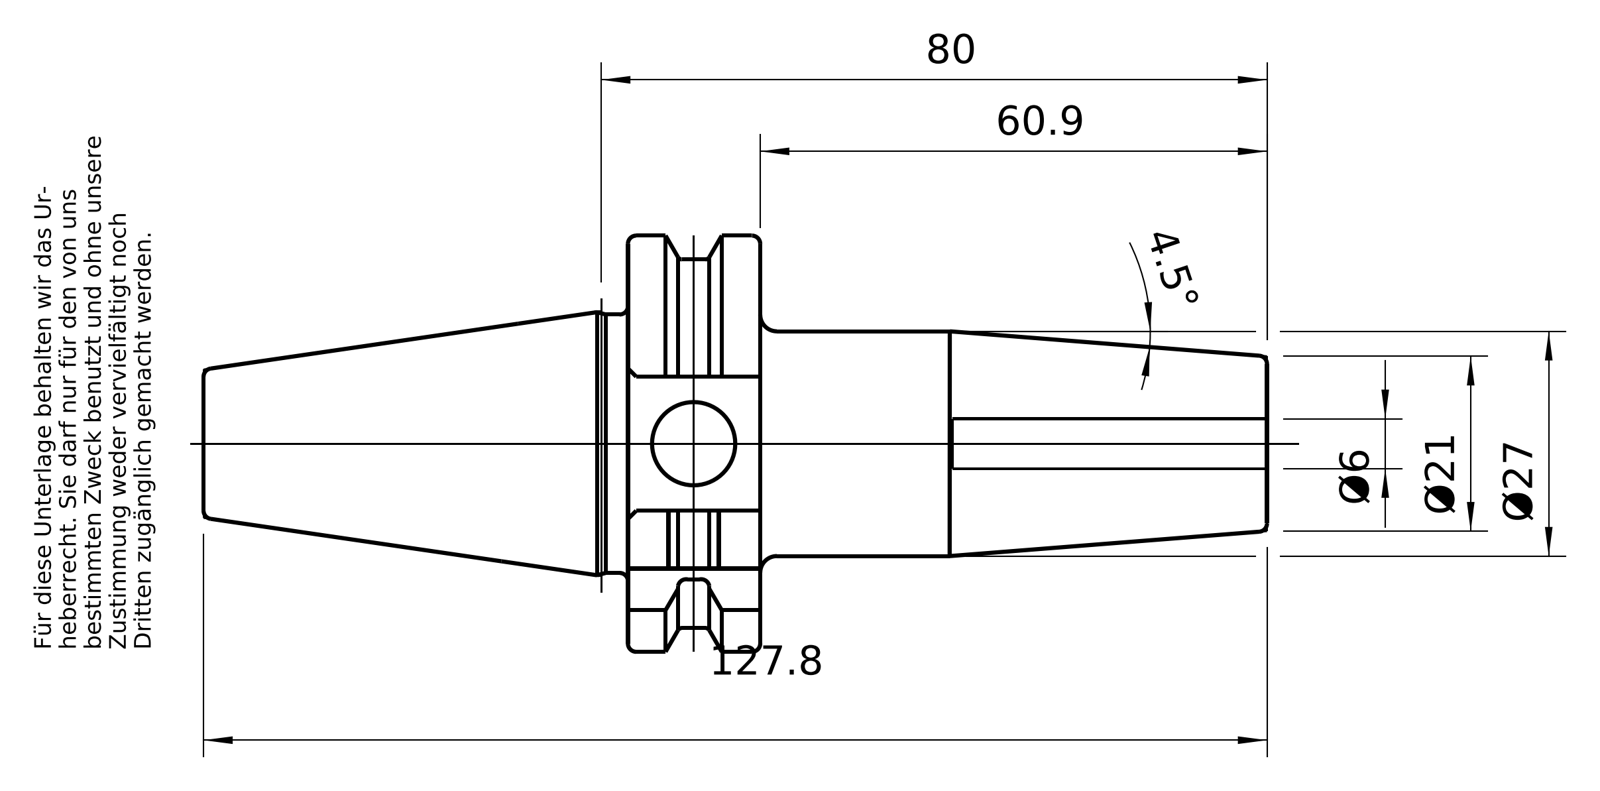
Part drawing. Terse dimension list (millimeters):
name: 30-440-06
written by: PRO/ENGINEER BY PARAMETRIC TECHNOLOGY CORPORATION, 2010430 (CONFIG_CONTROL_DESIGN)
unit: mm
bodies: 1 solid, 92 faces (21 planar, 23 cylindrical, 48 other)
size: 127.65 × 49.98 × 47.32
volume: 77 861 mm³; area: 17 066 mm²
holes: 1× ⌀6, 1× ⌀10.11, 1× ⌀13.01, 1× ⌀13.5
bosses: 1× ⌀31.05, 1× ⌀27, 1× ⌀12.01
rounds: 1× R22.02, 1× R24.99
face distances: 15.85, 60.95, 76.8, 35.1, 16.1, 6.95, 23.05, 3.8, 31.3, 50.85
